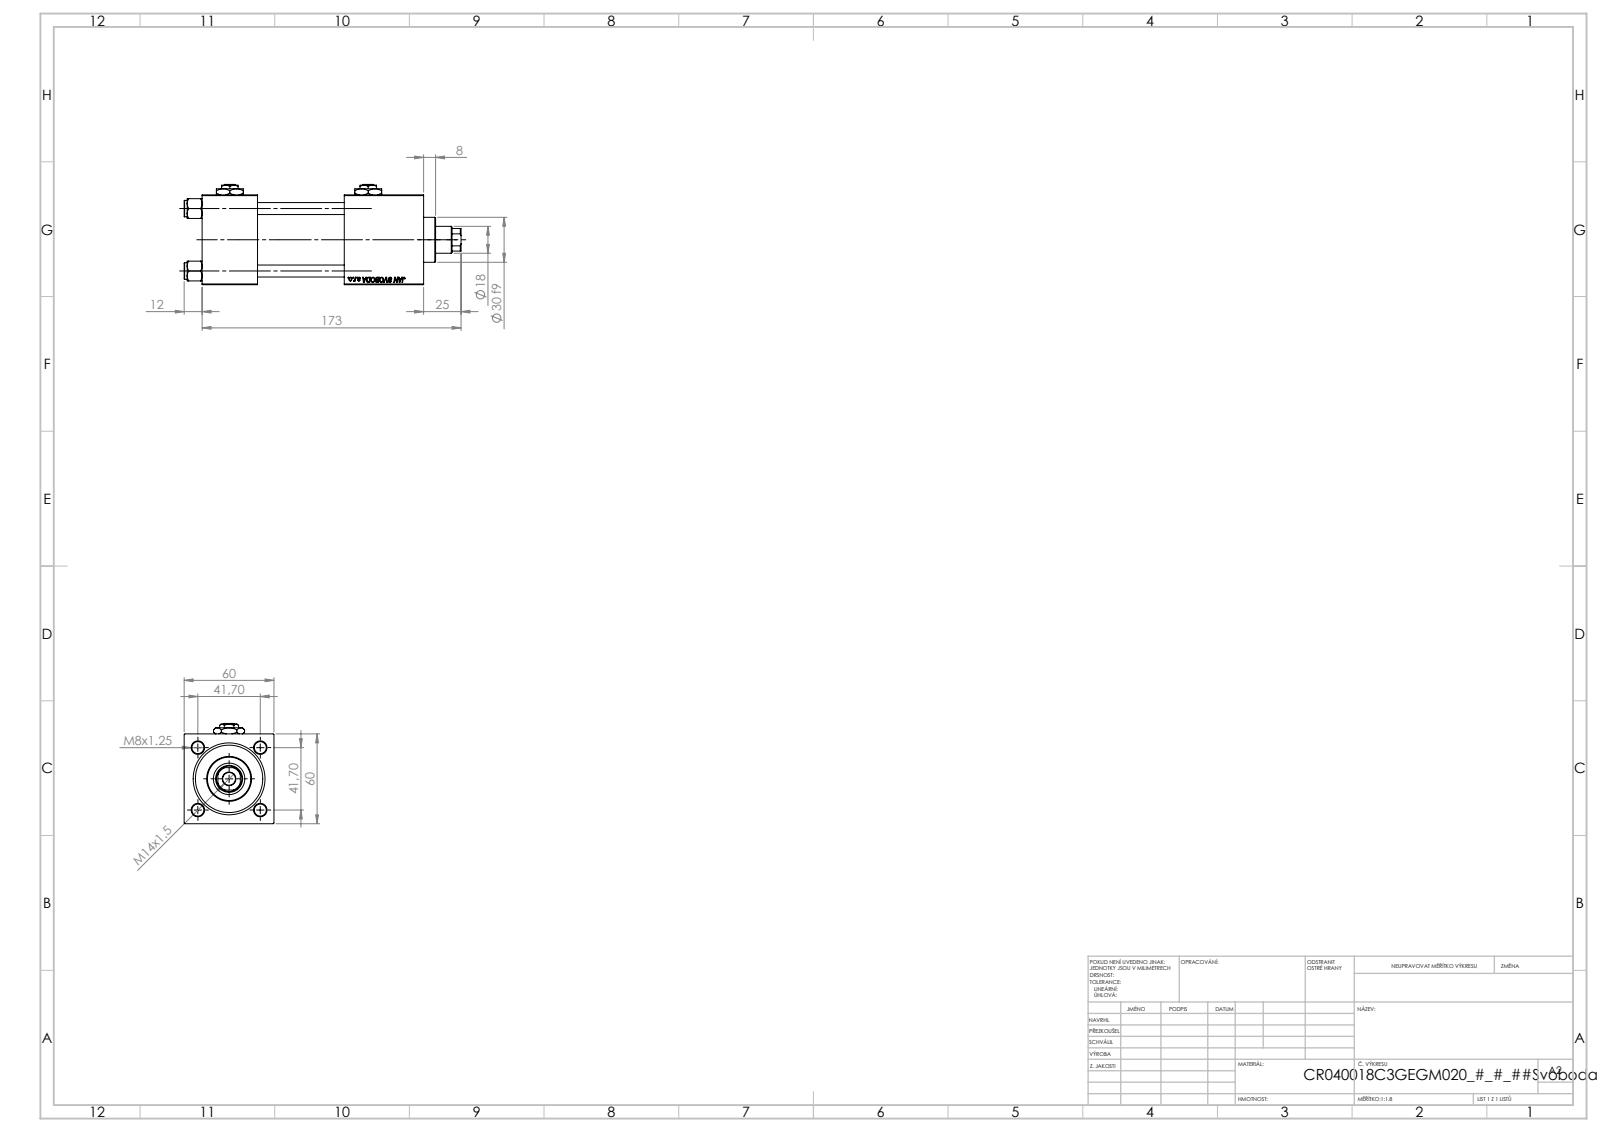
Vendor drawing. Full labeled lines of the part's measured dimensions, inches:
Part name (STEP PRODUCT): V215CR_C_TYCINKA; NUT_M5_C; V215CR_C_Body; V215CR_VCP_C (+2 more)
STEP written by: SolidWorks 2019 (CONFIG_CONTROL_DESIGN)
Units: inches
Bodies: 13 solids, 1250 faces (574 planar, 98 cylindrical, 578 other)
Overall size (bounding box): 7.283 × 2.638 × 2.362
Volume: 24.34 in³ · Surface area: 167.9 in²
Round holes (diameter × count): ⌀0.315 ×4, ⌀0.276 ×2, ⌀0.656 ×2, ⌀0.945 ×2, ⌀0.335 ×1, ⌀0.709 ×1, ⌀0.827 ×1, ⌀1.22 ×1, ⌀1.575 ×1, ⌀1.772 ×1
Round bosses / shafts (diameter × count): ⌀0.433 ×4, ⌀1.811 ×1, ⌀1.181 ×1
Partial cylindrical surfaces — rounded edges, fillets, slot ends (radius × count): R0.335 ×1
Main face-to-face distances: 2.362, 1.457, 2.087, 5.827, 4.37, 2.283, 3.74, 4.697, 3.24, 0.957
Hole centre spacings: 1.161, 1.642, 2.322, 3.642
